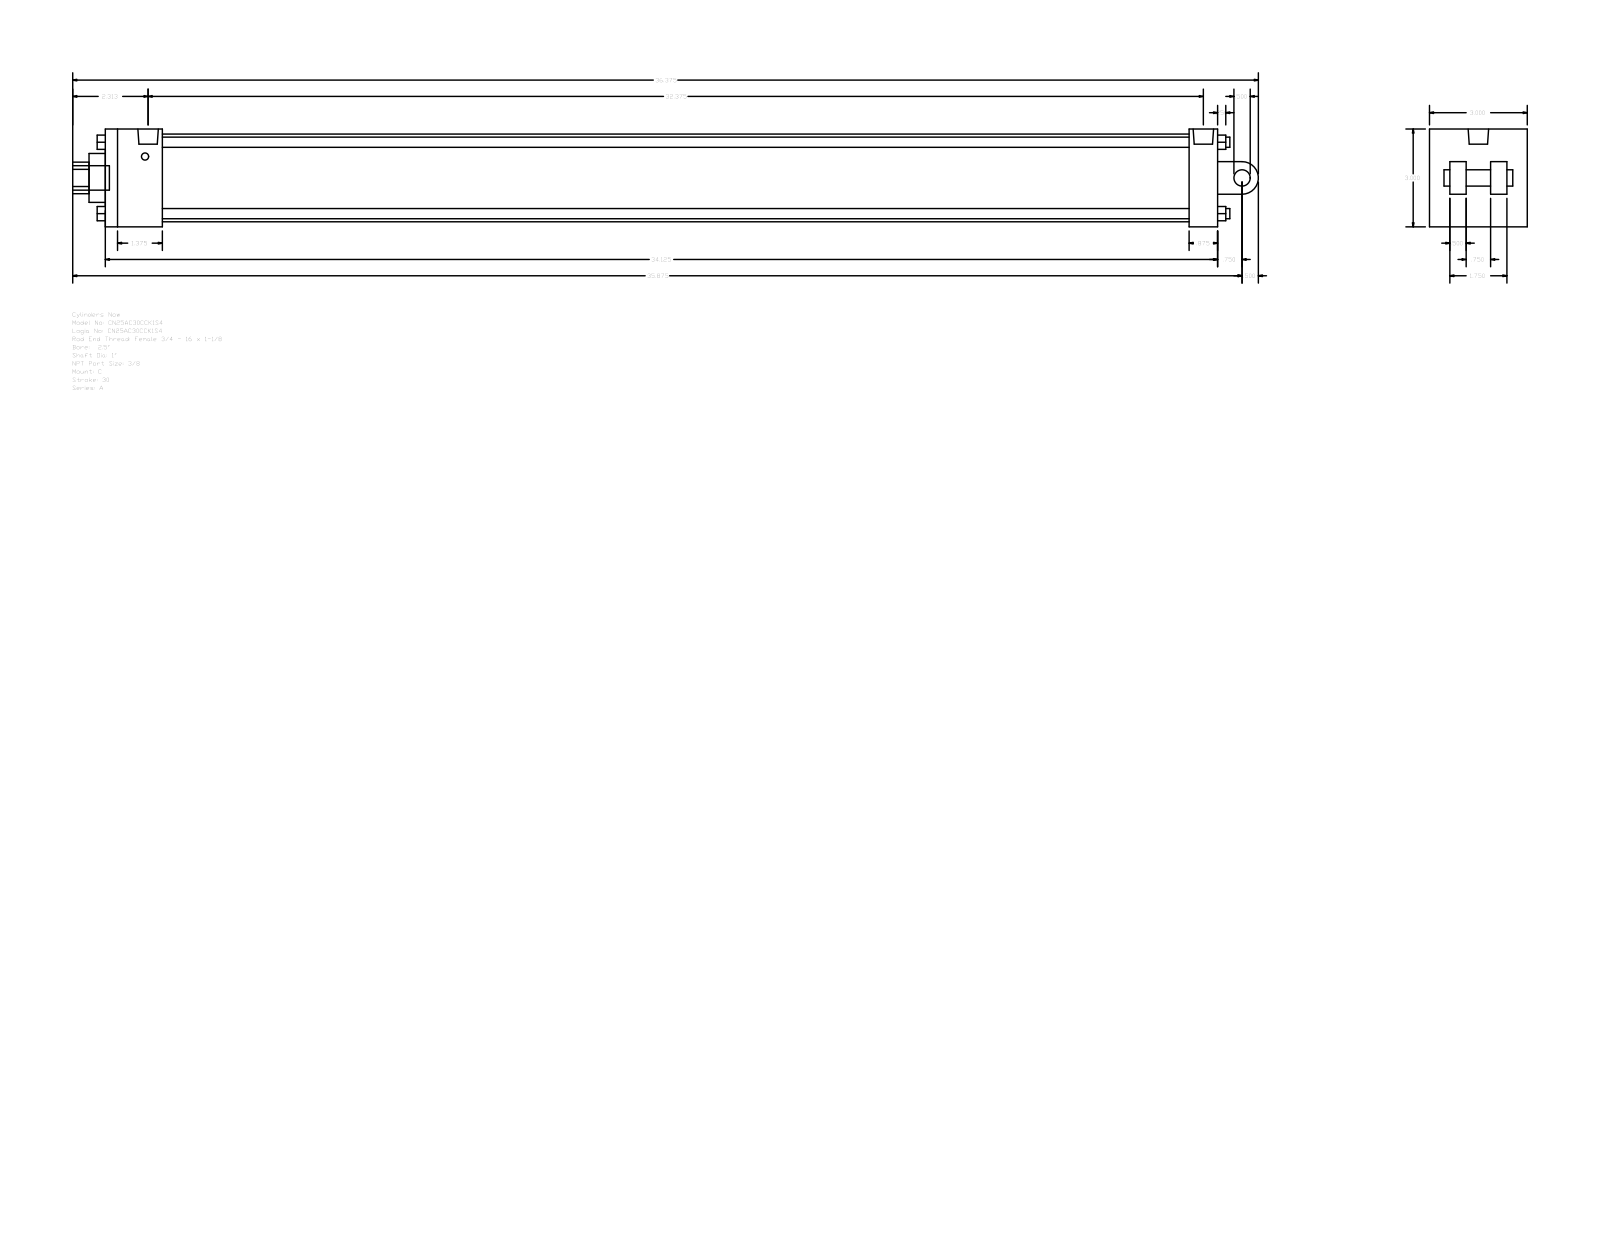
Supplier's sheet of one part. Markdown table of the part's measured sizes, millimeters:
| quantity | value |
| --- | --- |
| part name | A_C__0250_1 |
| STEP written by | GSSL Pune (CONFIG_CONTROL_DESIGN) |
| units | millimeters |
| bodies | 0 solids, 135 faces (102 planar, 33 cylindrical, 0 other) |
| overall size | 923.92 × 76.2 × 76.2 |
| round holes (diameter × count) | 5.56 × 2, 15.93 × 1, 25.4 × 1, 38.1 × 1, 68.33 × 1 |
| round bosses / shafts (diameter × count) | 7.94 × 4, 5.56 × 2, 19.05 × 1, 15.93 × 1, 12.7 × 1 |
| partial cylindrical surfaces (radius × count) | 12.29 × 1, 12.7 × 1 |
| main face-to-face distances | 76.2, 866.77, 12.7, 44.45, 844.55, 800.1, 822.32, 22.22, 15.87, 25.4 |
| hole center spacings | 2.38 |
